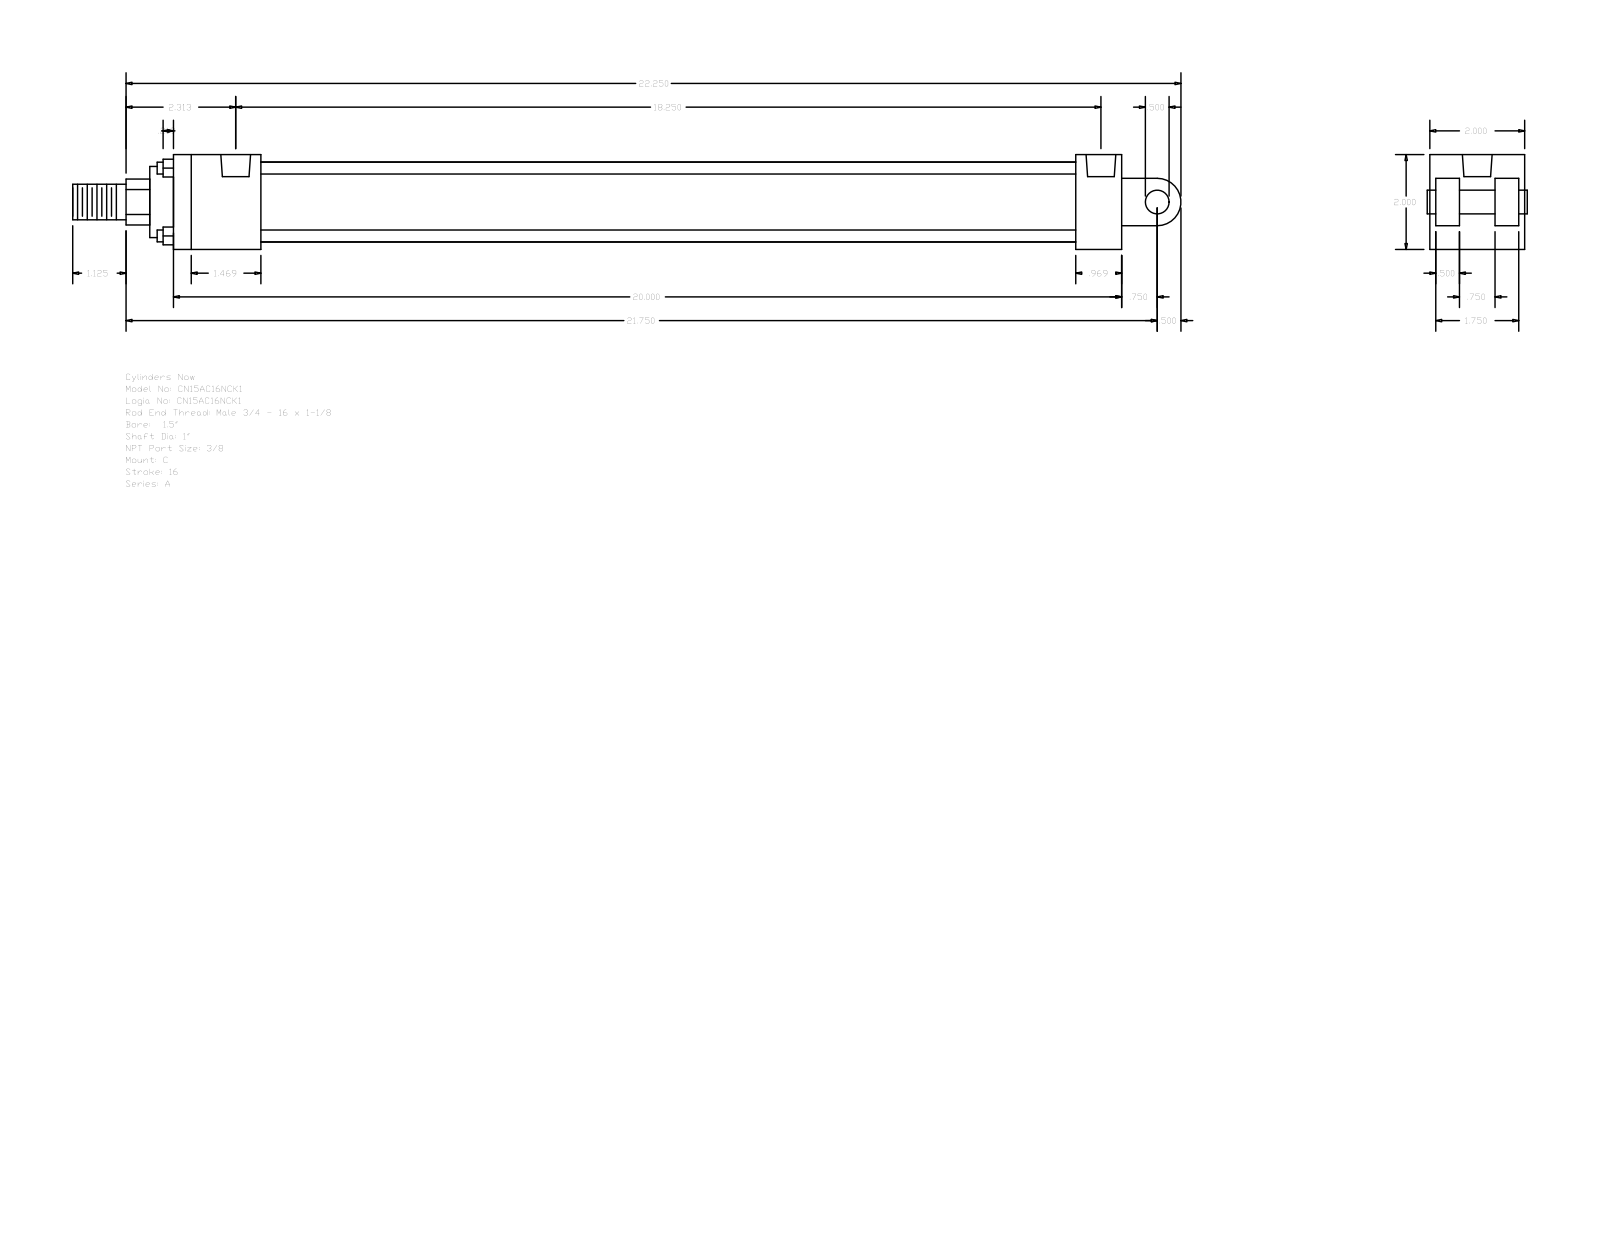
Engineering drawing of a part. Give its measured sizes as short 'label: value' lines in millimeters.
name: A_C__0150_1
written by: GSSL Pune (CONFIG_CONTROL_DESIGN)
unit: mm
bodies: 0 solids, 99 faces (70 planar, 29 cylindrical, 0 other)
size: 593.73 × 50.8 × 50.8
holes: 4× ⌀5.56, 2× ⌀15.93
bosses: 4× ⌀6.35, 1× ⌀42.93, 1× ⌀38.1, 1× ⌀25.4, 1× ⌀19.05, 1× ⌀12.7
rounds: 1× R12.29, 1× R12.7
face distances: 50.8, 12.7, 3.17, 15.87, 47.63, 34.93, 31.76, 508, 38.1, 483.39
hole spacings: 3.97, 455.61, 459.58, 463.55
